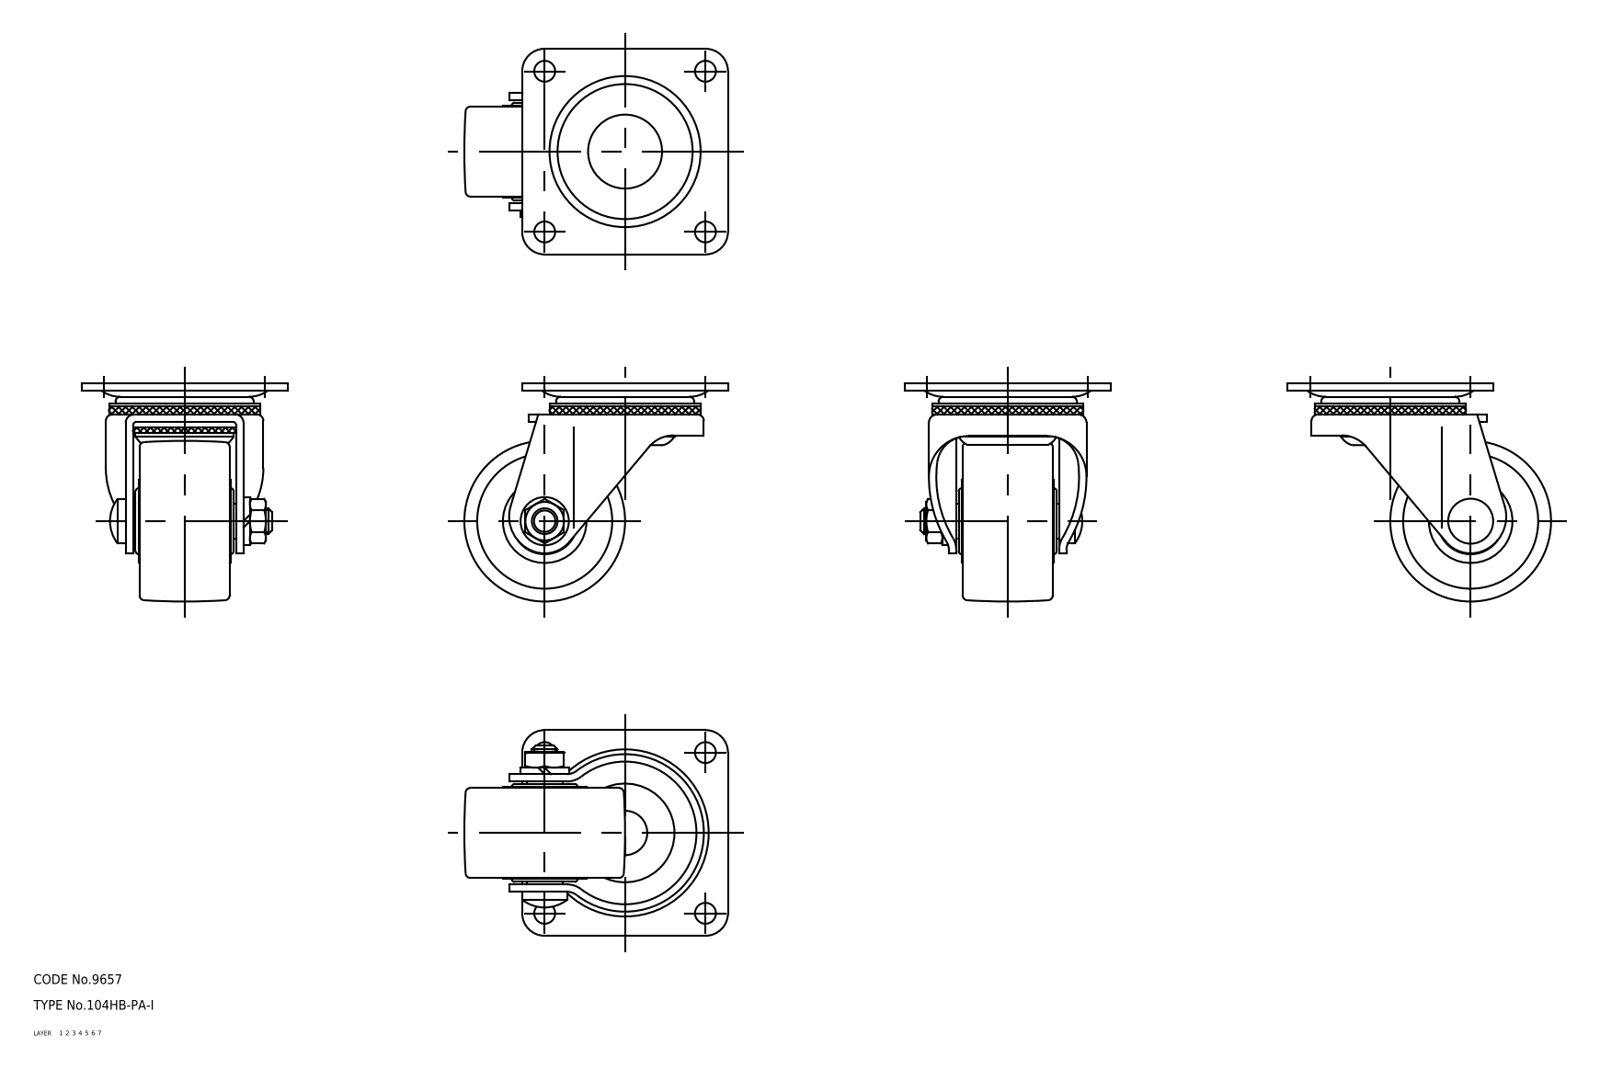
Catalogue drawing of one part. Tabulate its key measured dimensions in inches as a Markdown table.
| quantity | value |
| --- | --- |
| part name | 67122653; 67122666; 67122679; 67122692 (+1 more) |
| STEP written by | CADfix (AUTOMOTIVE_DESIGN) |
| units | inches |
| bodies | 5 solids, 197 faces (0 planar, 0 cylindrical, 197 other) |
| overall size | 3.228 × 2.677 × 2.52 |
| volume | 5.797 in³ |
| surface area | 52.11 in² |
